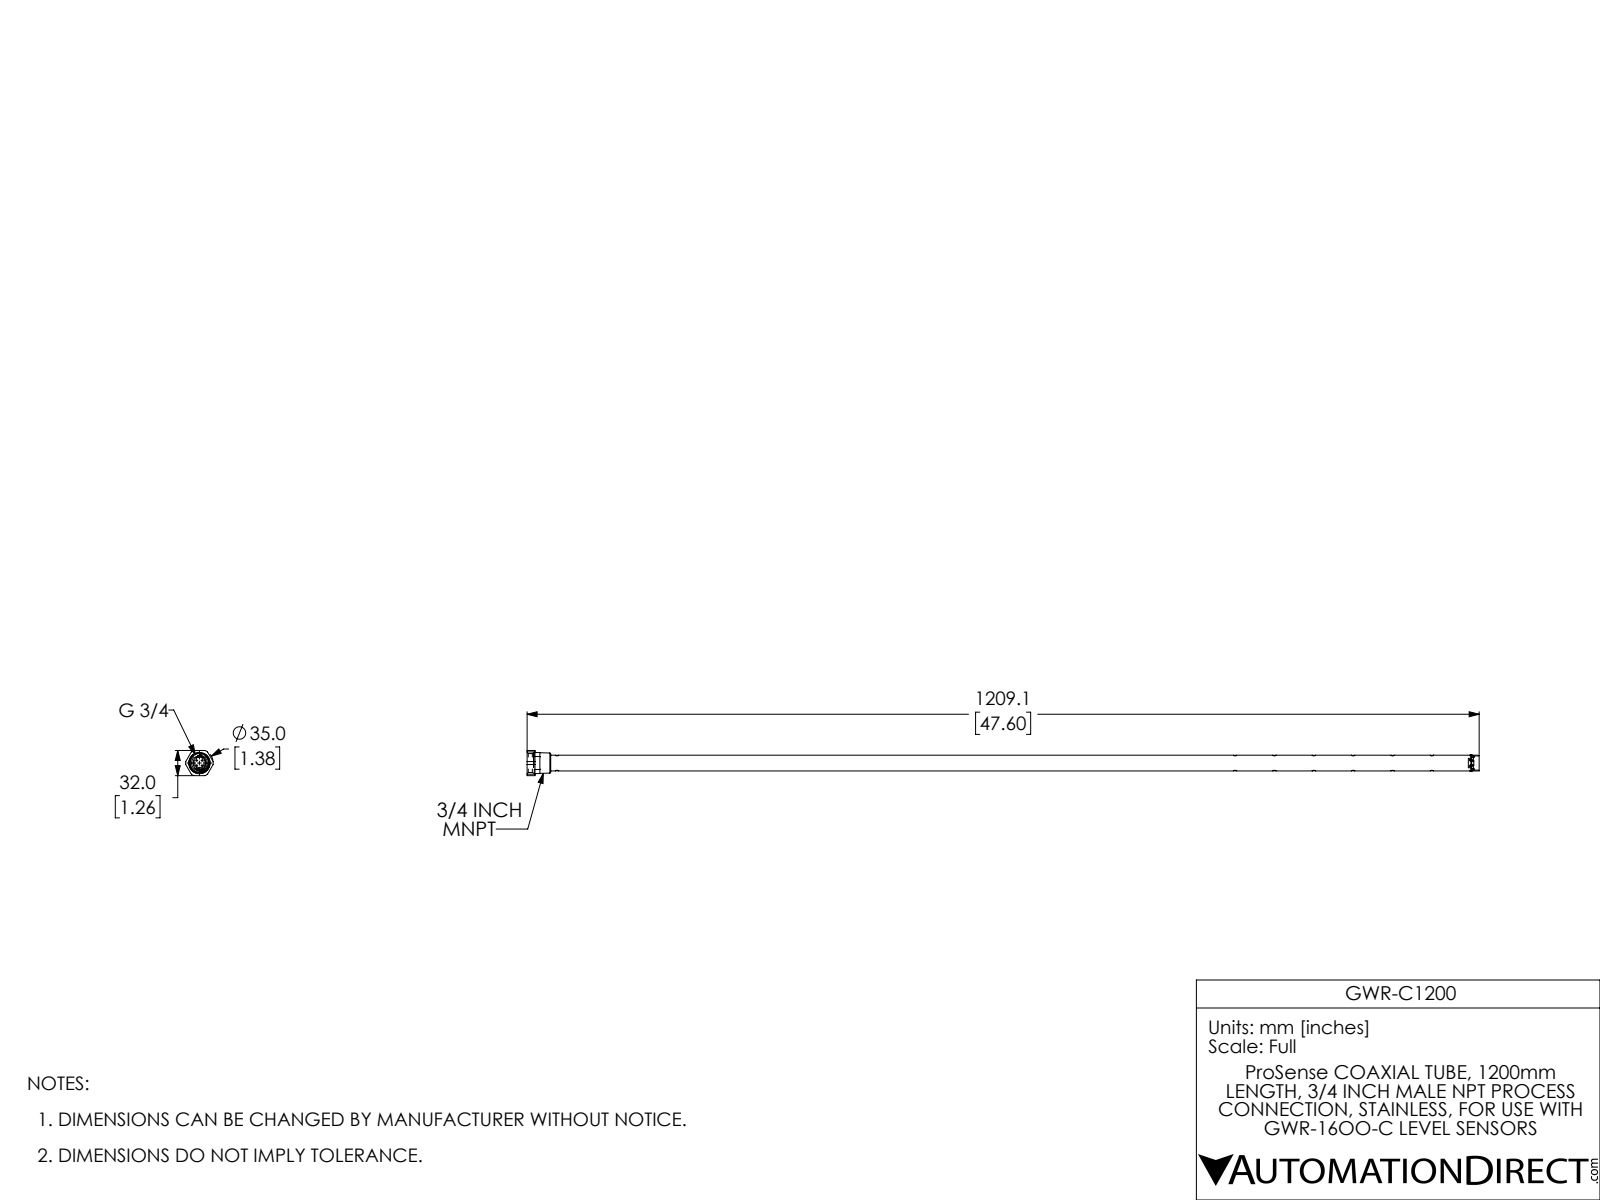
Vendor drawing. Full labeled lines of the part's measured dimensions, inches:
Part name (STEP PRODUCT): GWR-C1200
STEP written by: SolidWorks 2017 (AUTOMOTIVE_DESIGN)
Units: inches
Bodies: 1 solid, 150 faces (23 planar, 101 cylindrical, 26 other)
Overall size (bounding box): 47.602 × 1.378 × 1.26
Volume: 23.25 in³ · Surface area: 125.5 in²
Round holes (diameter × count): ⌀0.157 ×8, ⌀0.469 ×1, ⌀0.65 ×1, ⌀0.709 ×1, ⌀0.95 ×1
Round bosses / shafts (diameter × count): ⌀0.039 ×2, ⌀1.053 ×1, ⌀0.787 ×1, ⌀0.701 ×1
Partial cylindrical surfaces — rounded edges, fillets, slot ends (radius × count): R0.075 ×8, R0.159 ×1, R0.295 ×1, R0.37 ×1, R0.374 ×1, R0.689 ×1
Main face-to-face distances: 1.26, 0.394, 0.035, 0.358, 0.28, 0.315, 0.673, 47.209, 0.508, 0.787
Hole centre spacings: 1.969, 3.937, 5.906, 7.874, 9.843, 11.811, 33.898, 35.866
